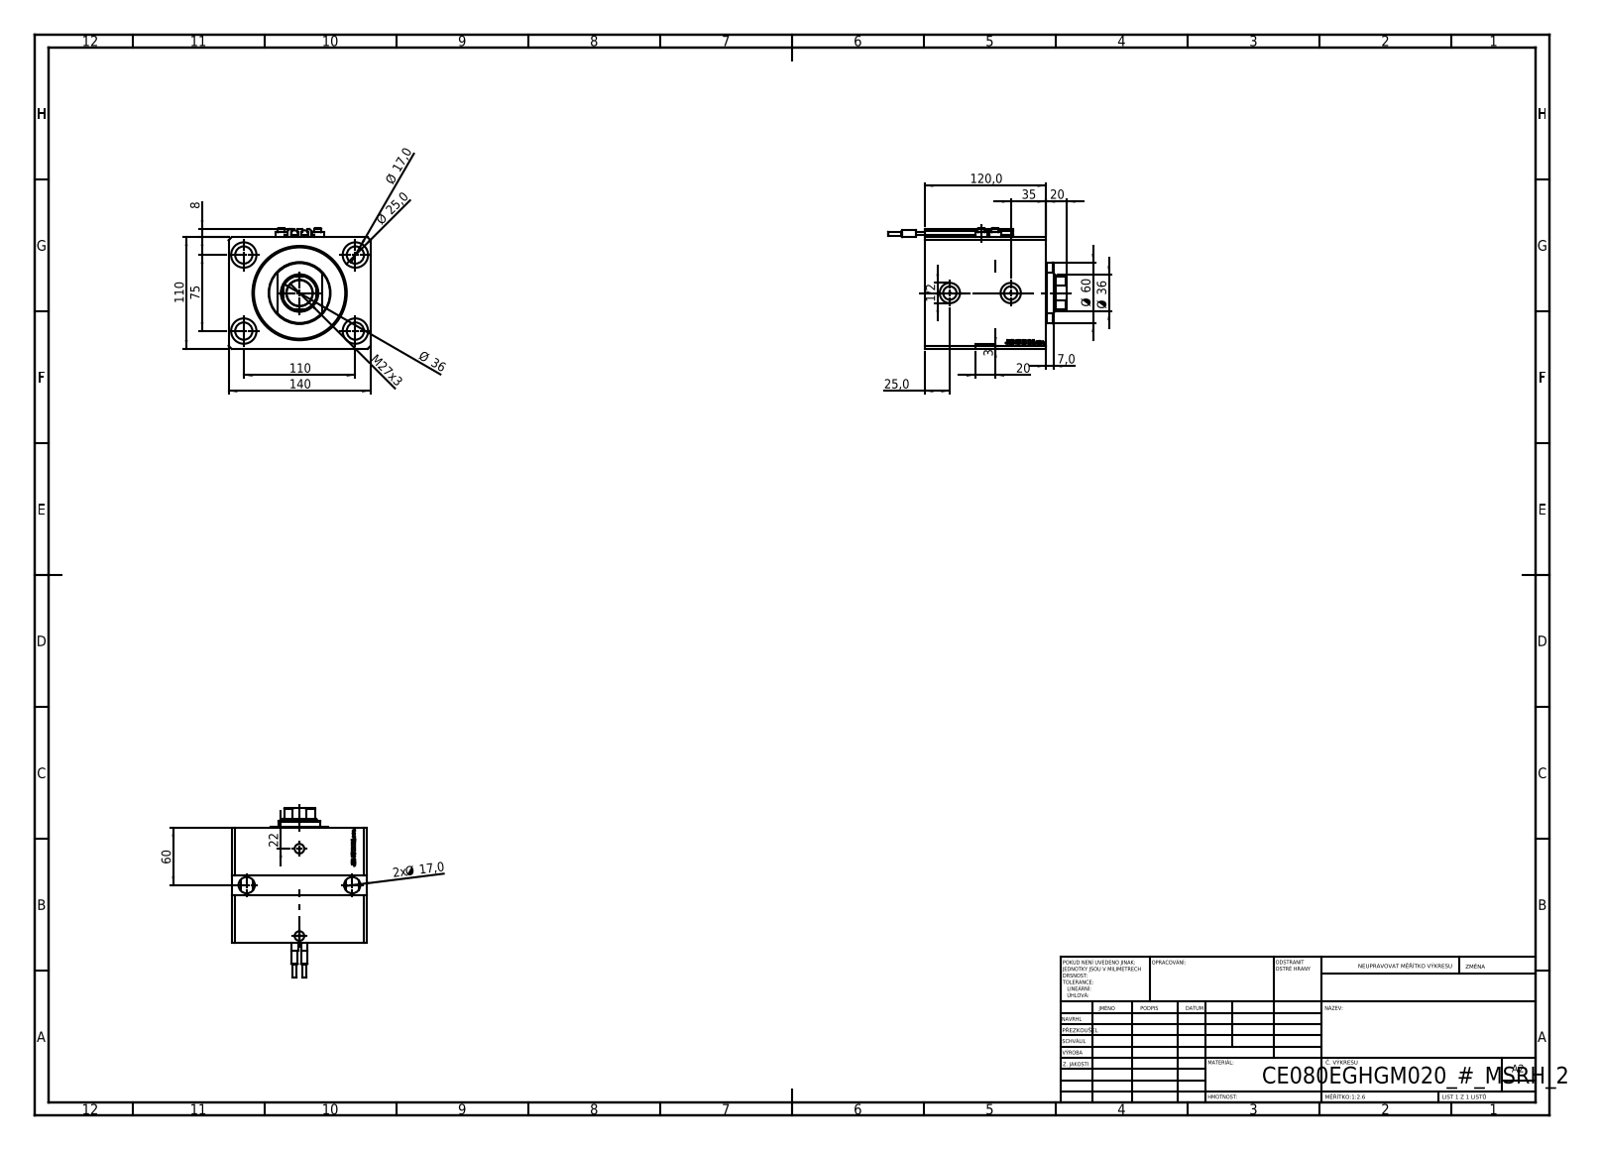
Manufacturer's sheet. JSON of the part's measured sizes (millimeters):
{"part_name": "V250CE_E_Body; V250CE_VC_E; ALLEN BOLT V250CE; SWITCH_V250CE (+1 more)", "step_written_by": "SolidWorks 2019 (CONFIG_CONTROL_DESIGN)", "units": "millimeters", "bodies": {"solids": 10, "faces": 1164, "planar": 580, "cylindrical": 138, "other": 446}, "overall_size": [176, 140, 119], "volume_mm3": 1594000, "surface_area_mm2": 220017, "round_holes": [[17, 6], [1.25, 4], [4, 4], [25, 4], [10, 2], [13.16, 2], [20, 2], [25.5, 1], [36, 1], [80, 1], [93, 1]], "round_bosses_or_shafts": [[11.6, 4], [7, 4], [6.8, 2], [6.5, 2], [4, 2], [60, 1]], "partial_cylinders_radius": [[0.2, 10], [17.5, 1]], "face_to_face_distances": [110, 20, 140, 25, 95, 120, 100, 75, 40, 55], "hole_center_spacings": [66.57, 110, 13.6, 33.62, 36, 37.22, 38.23, 38.48]}
